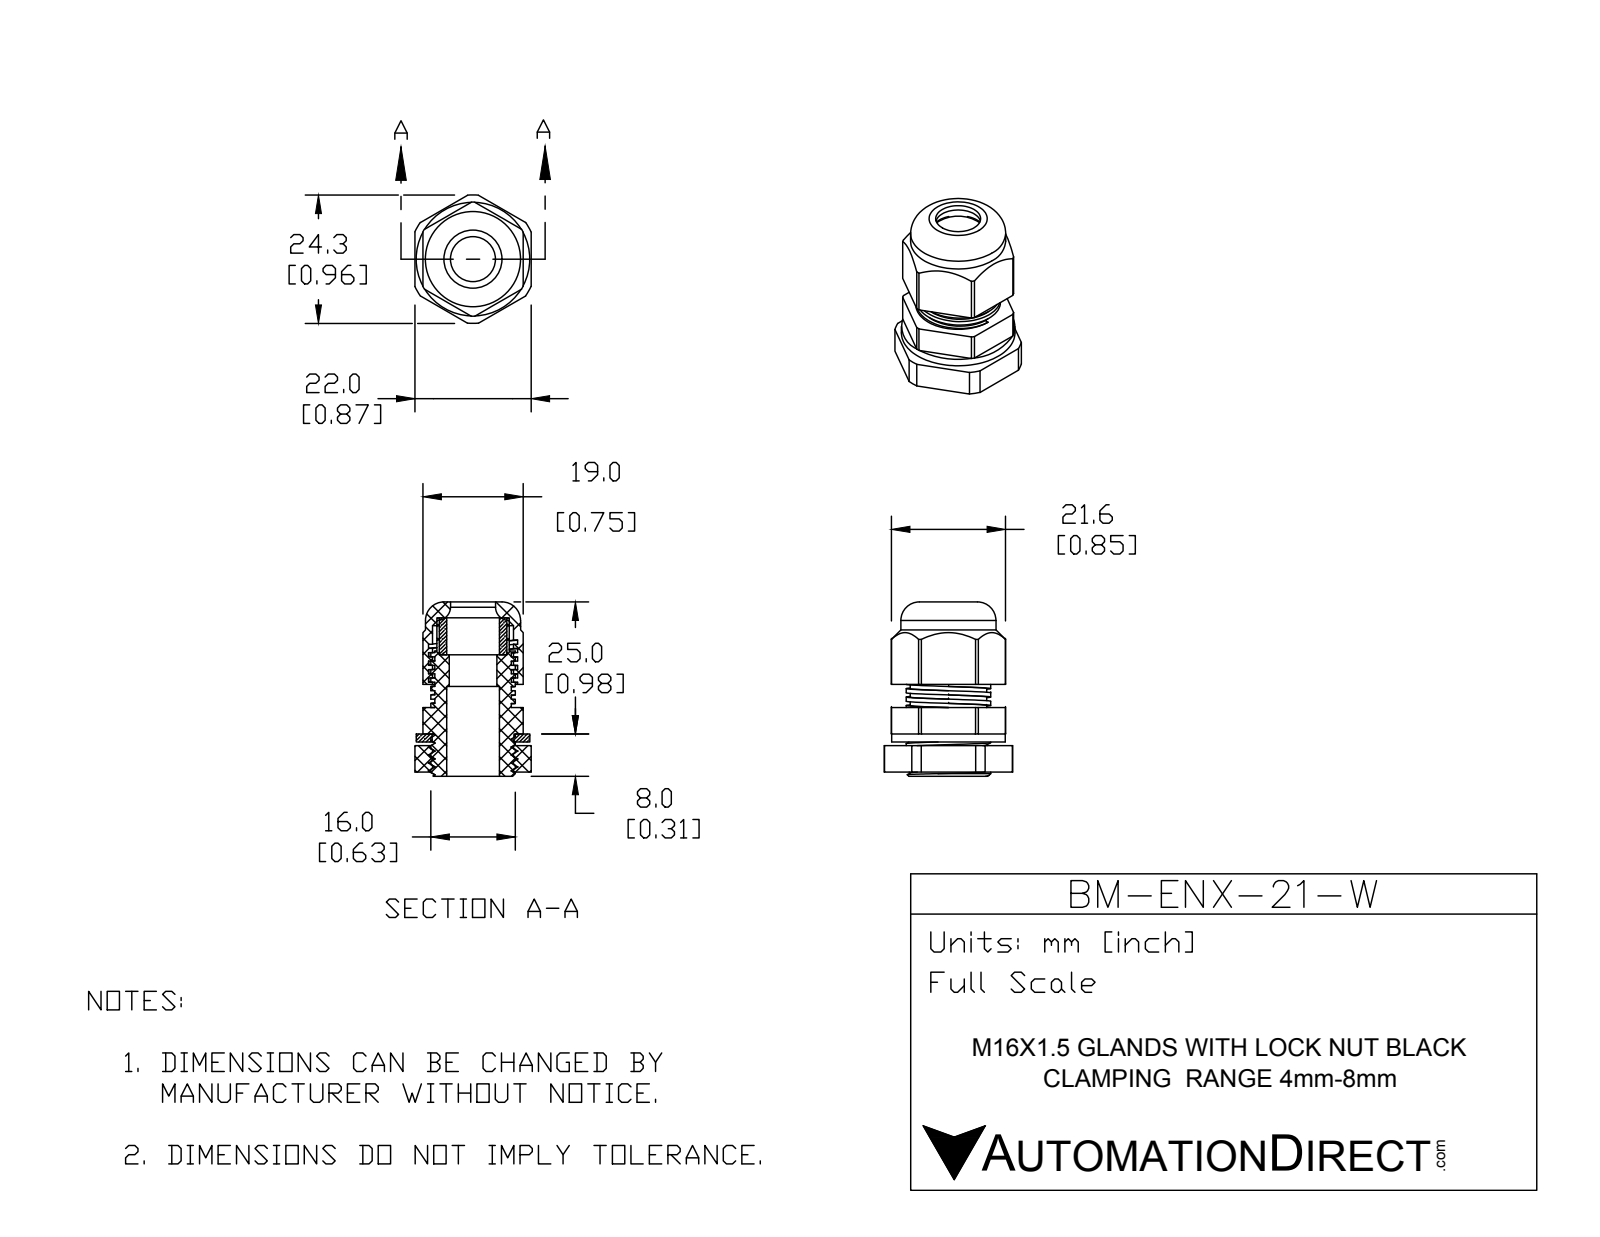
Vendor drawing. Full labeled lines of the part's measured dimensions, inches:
Part name (STEP PRODUCT): BM-ENX-21-W
STEP written by: SolidWorks 2015 (CONFIG_CONTROL_DESIGN)
Units: inches
Bodies: 5 solids, 243 faces (133 planar, 88 cylindrical, 22 other)
Overall size (bounding box): 1.299 × 0.957 × 0.866
Volume: 0.414 in³ · Surface area: 13.04 in²
Round holes (diameter × count): ⌀0.335 ×1, ⌀0.354 ×1, ⌀0.394 ×1, ⌀0.504 ×1, ⌀0.604 ×1, ⌀0.61 ×1
Round bosses / shafts (diameter × count): ⌀0.846 ×1, ⌀0.709 ×1, ⌀0.63 ×1, ⌀0.539 ×1
Partial cylindrical surfaces — rounded edges, fillets, slot ends (radius × count): R0.425 ×1, R0.478 ×1
Main face-to-face distances: 0.059, 0.748, 0.197, 0.295, 0.807, 0.256, 0.866, 0.098, 0.236, 0.039
